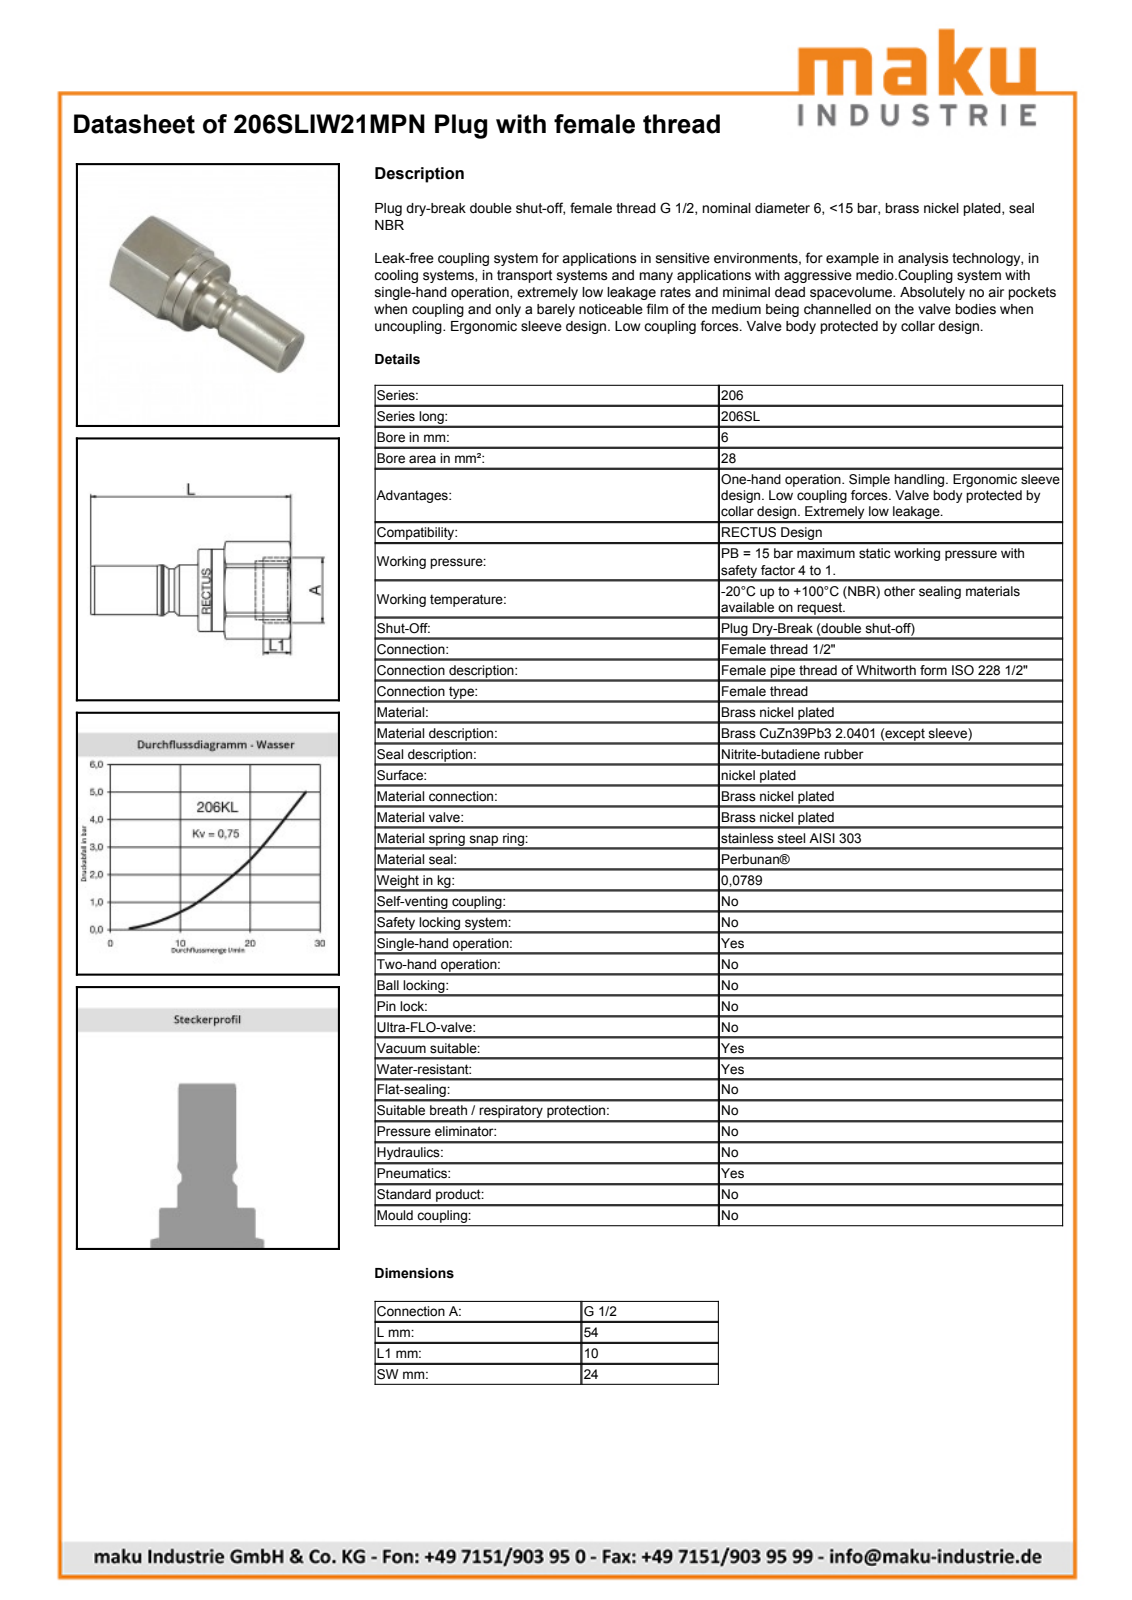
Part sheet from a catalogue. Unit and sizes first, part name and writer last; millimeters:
Units: millimetres
Overall size (bounding box): 54.15 × 26.77 × 25.9
Round holes (diameter × count): ⌀10.2 ×1, ⌀17 ×1, ⌀18.63 ×1
Round bosses / shafts (diameter × count): ⌀21 ×1, ⌀16.65 ×1, ⌀15.08 ×1, ⌀12.95 ×1, ⌀12.5 ×1, ⌀11 ×1
Partial cylindrical surfaces — rounded edges, fillets, slot ends (radius × count): R13.53 ×1
Main face-to-face distances: 24, 24.02, 14.65, 27.5, 42.15, 54.15, 26.65, 12, 34.15, 6.65
Volume: 12 259 mm³ · Surface area: 5 257 mm²
Bodies: 1 solid, 65 faces (18 planar, 19 cylindrical, 28 other)
Part name (STEP PRODUCT): D110485
STEP written by: Autodesk Inventor 2013 (AUTOMOTIVE_DESIGN)
